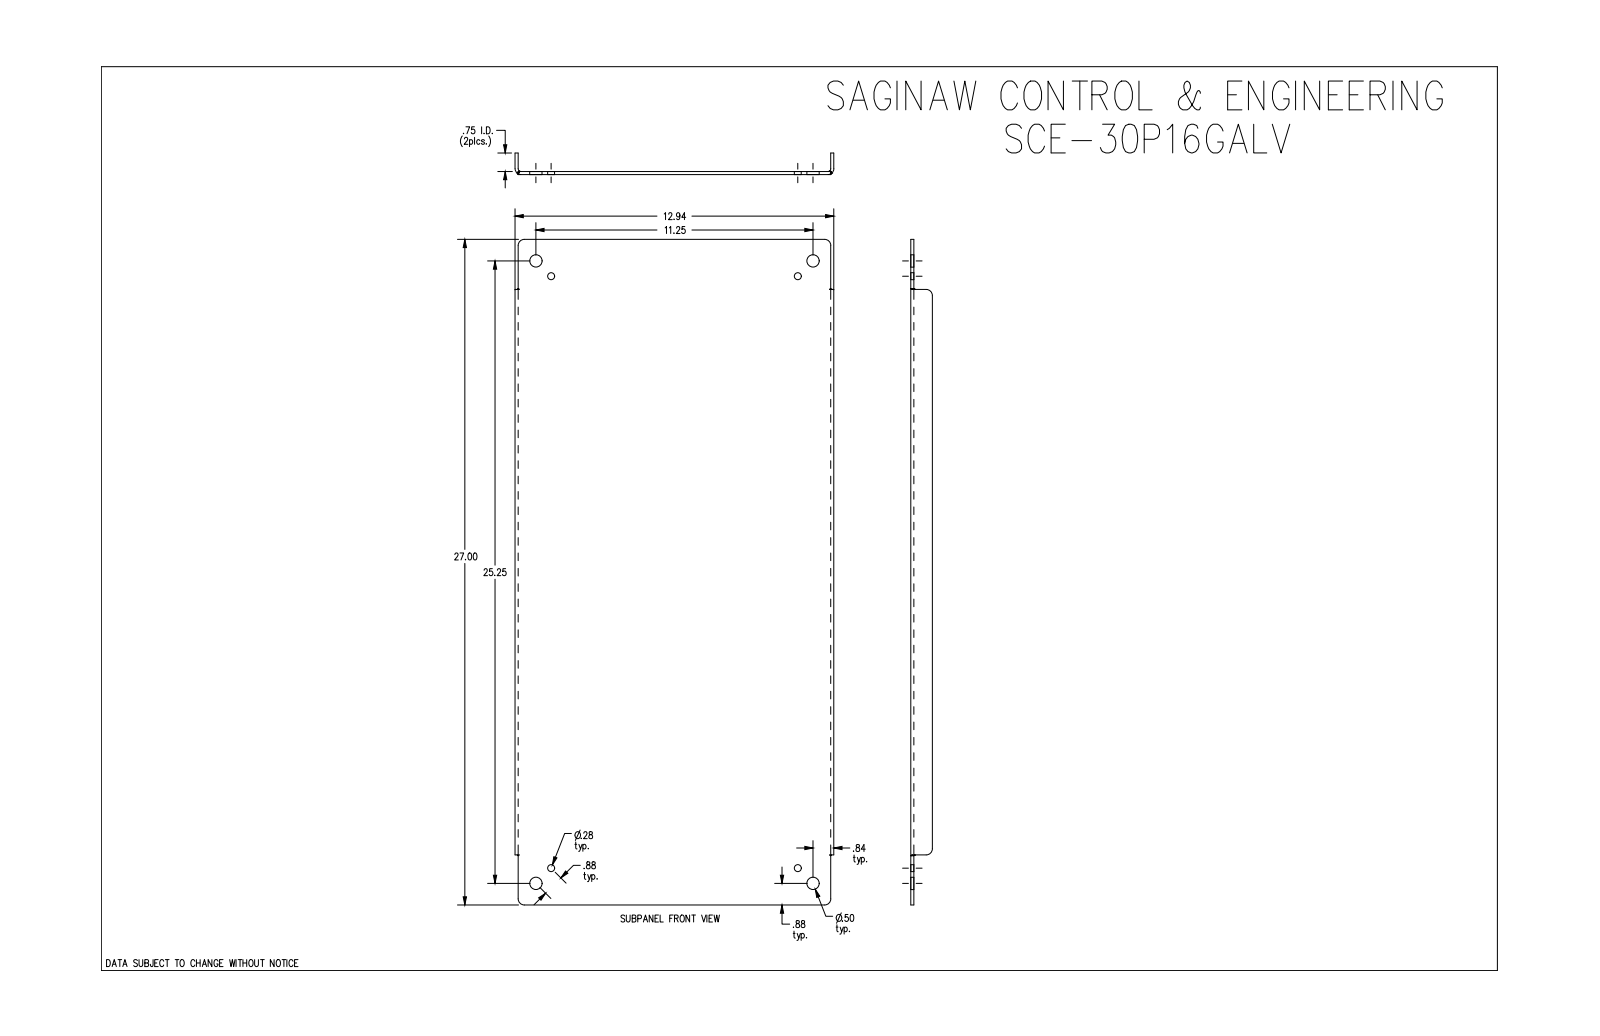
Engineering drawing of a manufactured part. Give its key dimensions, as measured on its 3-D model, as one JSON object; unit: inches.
{"part_name": "SCE-30P16GALV", "step_written_by": "SolidWorks 2019 (CONFIG_CONTROL_DESIGN)", "units": "inches", "bodies": {"solids": 1, "faces": 50, "planar": 18, "cylindrical": 20, "other": 12}, "overall_size": [27, 12.938, 0.875], "volume_in3": 47.27, "surface_area_in2": 767.7, "round_holes": [[0.281, 4], [0.5, 4]], "partial_cylinders_radius": [[0.25, 6], [0.112, 2], [0.237, 2]], "face_to_face_distances": [0.125, 0.125, 12.813, 12.687, 12.938, 0.75, 0.875, 27, 2.031, 24.969], "hole_center_spacings": [0.875, 10.65, 24.639, 26.828, 10.013, 11.25, 24.013, 25.25]}
